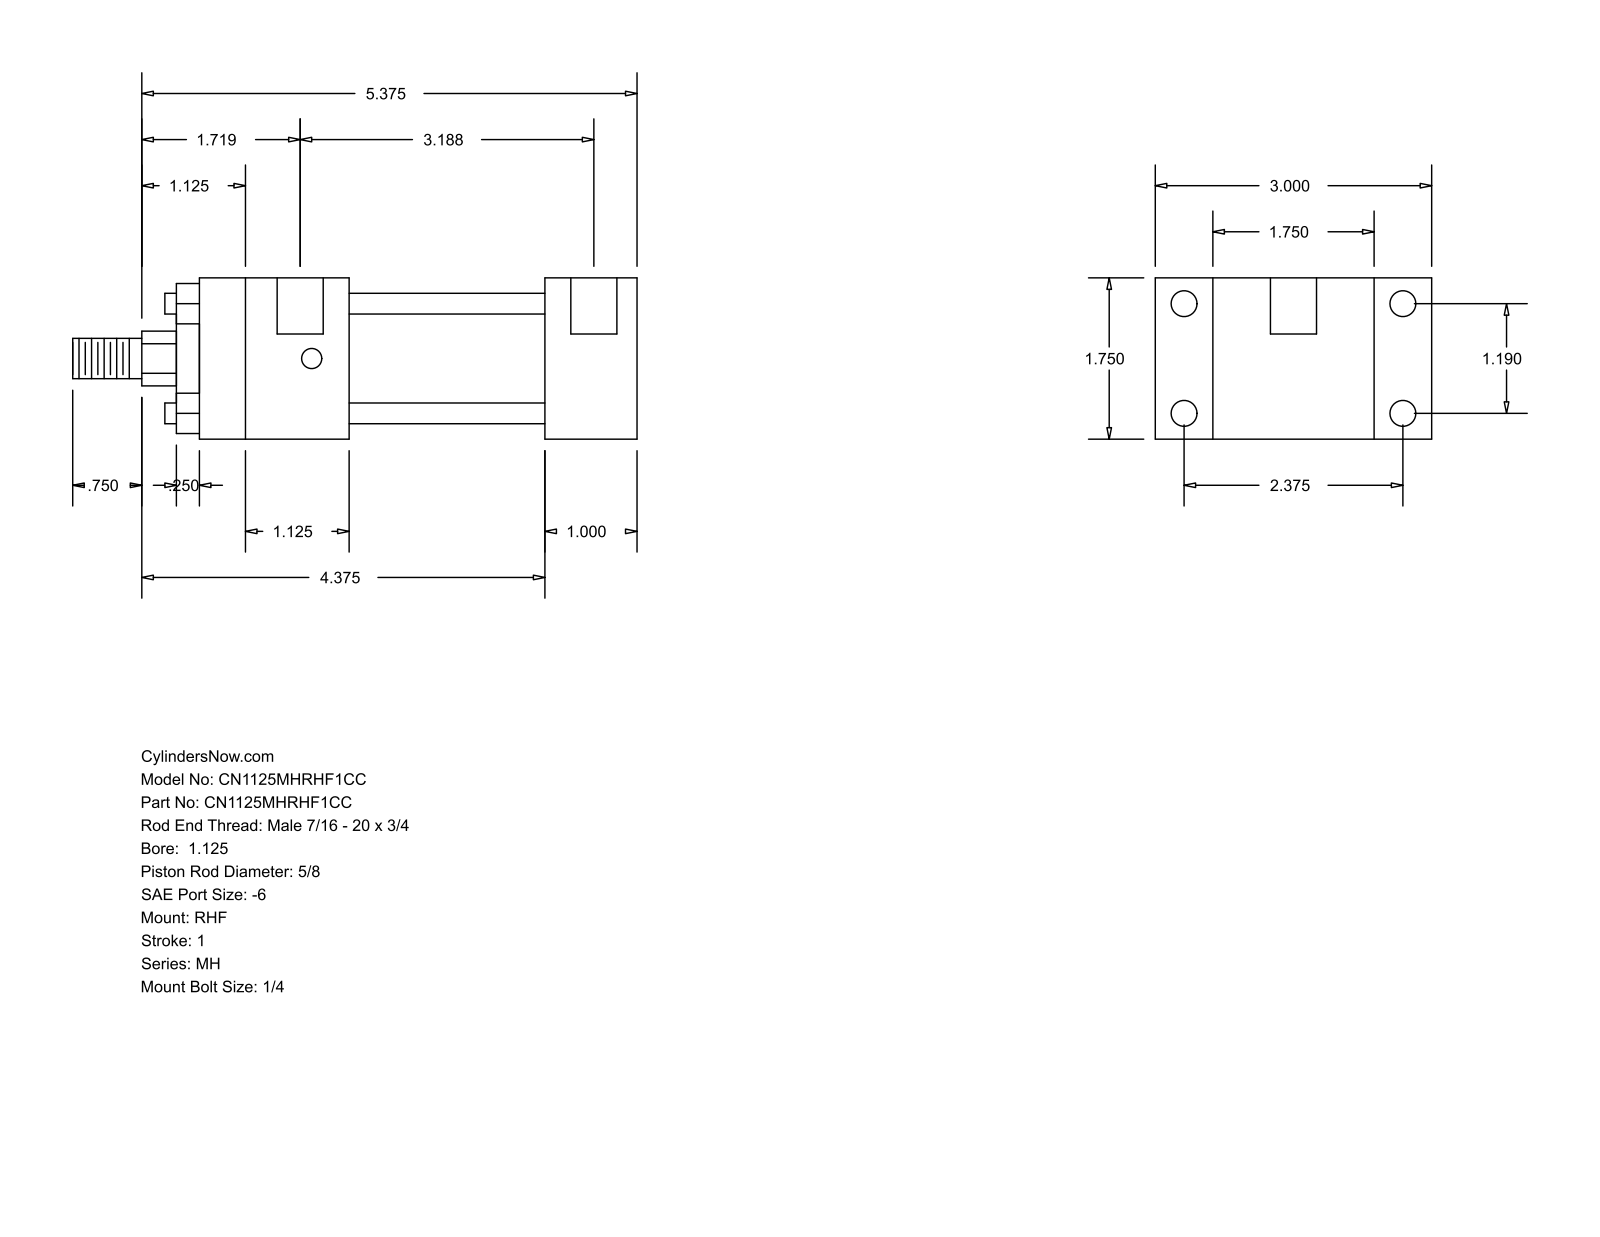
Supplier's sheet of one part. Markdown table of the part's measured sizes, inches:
| quantity | value |
| --- | --- |
| part name | MH_RHF__0112_0.625 |
| STEP written by | GSSL Pune (CONFIG_CONTROL_DESIGN) |
| units | inches |
| bodies | 0 solids, 88 faces (60 planar, 28 cylindrical, 0 other) |
| overall size | 6.125 × 3 × 1.75 |
| round holes (diameter × count) | 0.219 × 4, 0.281 × 4, 0.5 × 2 |
| round bosses / shafts (diameter × count) | 0.225 × 4, 1.375 × 1, 1.125 × 1, 0.625 × 1, 0.437 × 1 |
| partial cylindrical surfaces (radius × count) | 0.297 × 1 |
| main face-to-face distances | 1.75, 0.625, 2.375, 1, 3, 2.125, 3.125, 1.625, 3.75, 4.75 |
| hole center spacings | 1.19, 2.375, 2.656, 3.063, 0.125, 3.187 |
